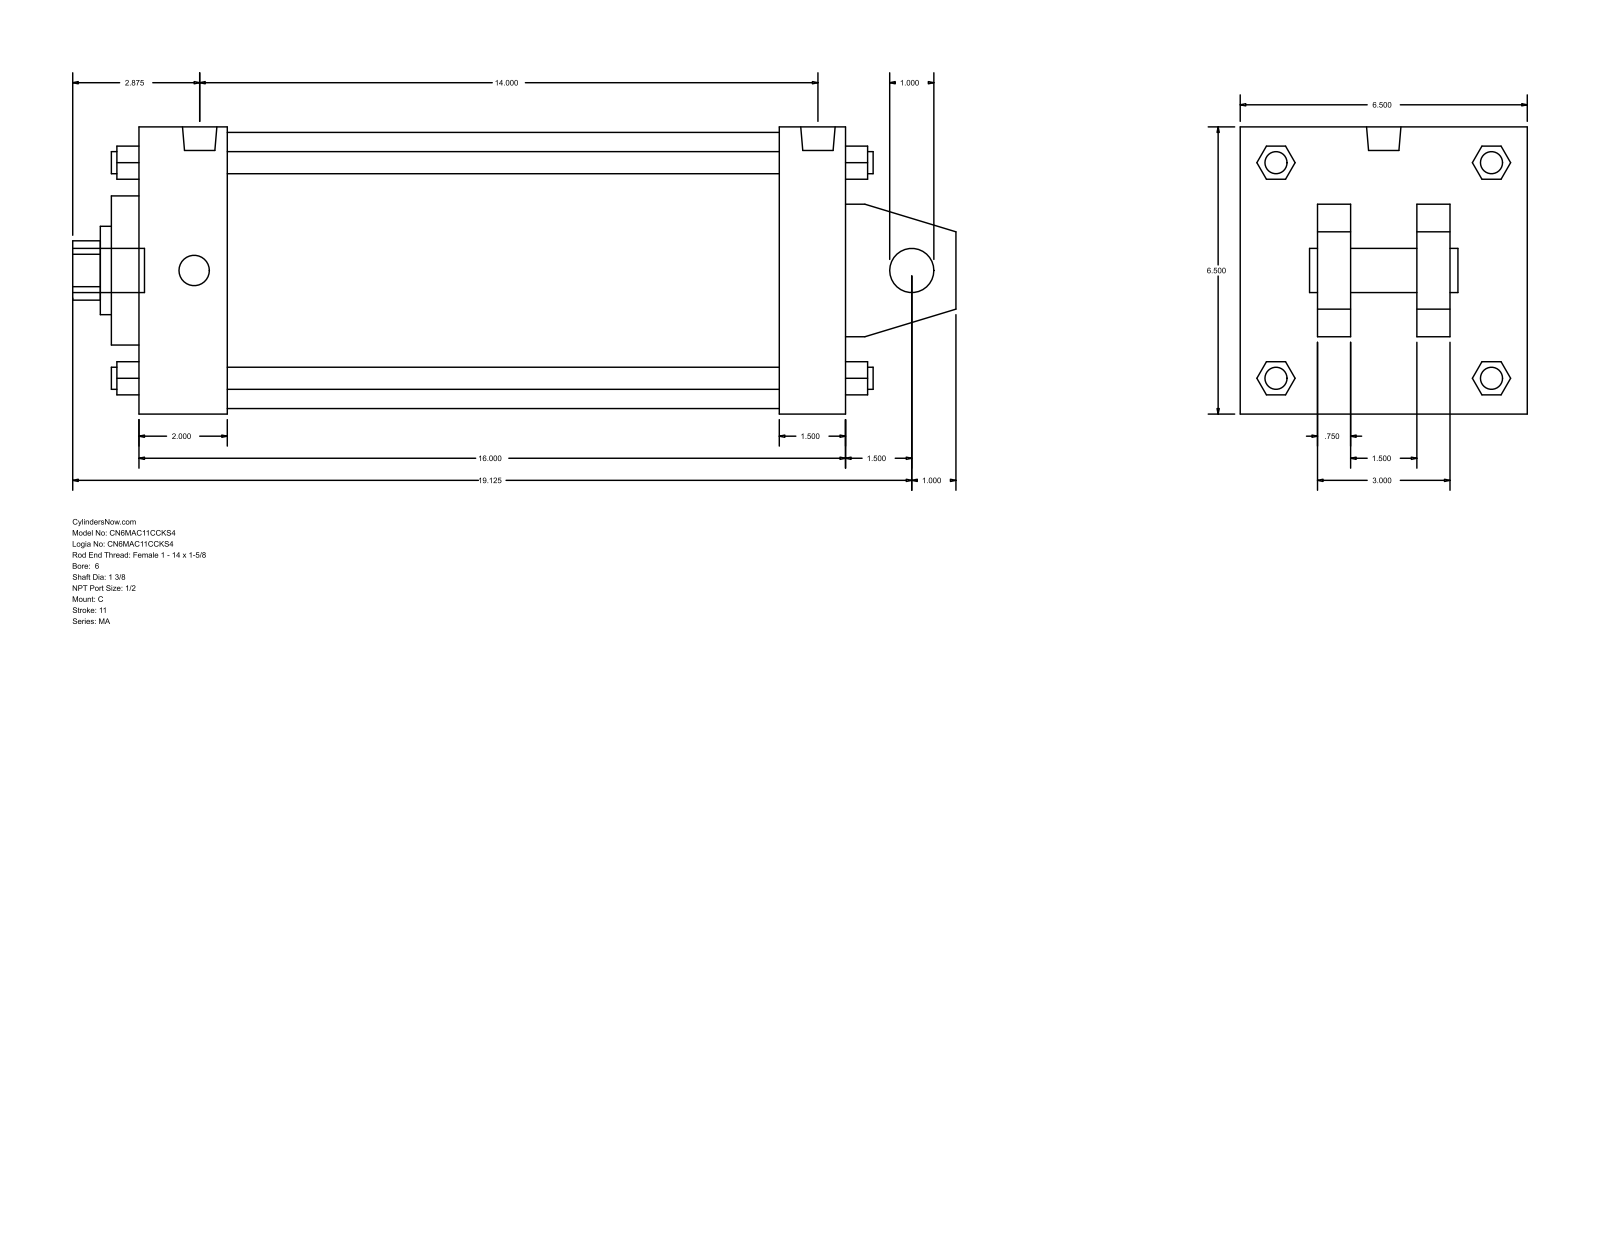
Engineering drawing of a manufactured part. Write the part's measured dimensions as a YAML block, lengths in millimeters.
part_name: "MA_C__0600_1.375"
step_written_by: "GSSL Pune (CONFIG_CONTROL_DESIGN)"
units: millimeters
bodies: {solids: 0, faces: 141, planar: 109, cylindrical: 32, other: 0}
overall_size: [508, 165.1, 165.1]
round_holes:
  - {diameter: 25.4, count: 1}
  - {diameter: 34.92, count: 1}
  - {diameter: 50.8, count: 1}
  - {diameter: 85.72, count: 1}
  - {diameter: 158.75, count: 1}
round_bosses_or_shafts:
  - {diameter: 17.46, count: 4}
  - {diameter: 12.7, count: 4}
  - {diameter: 19.77, count: 2}
  - {diameter: 25.4, count: 1}
partial_cylinders:
  - {radius: 17.06, count: 1}
face_to_face_distances: [165.1, 406.4, 38.1, 19.05, 63.5, 101.6, 50.8, 120.65, 44.45, 368.3]
